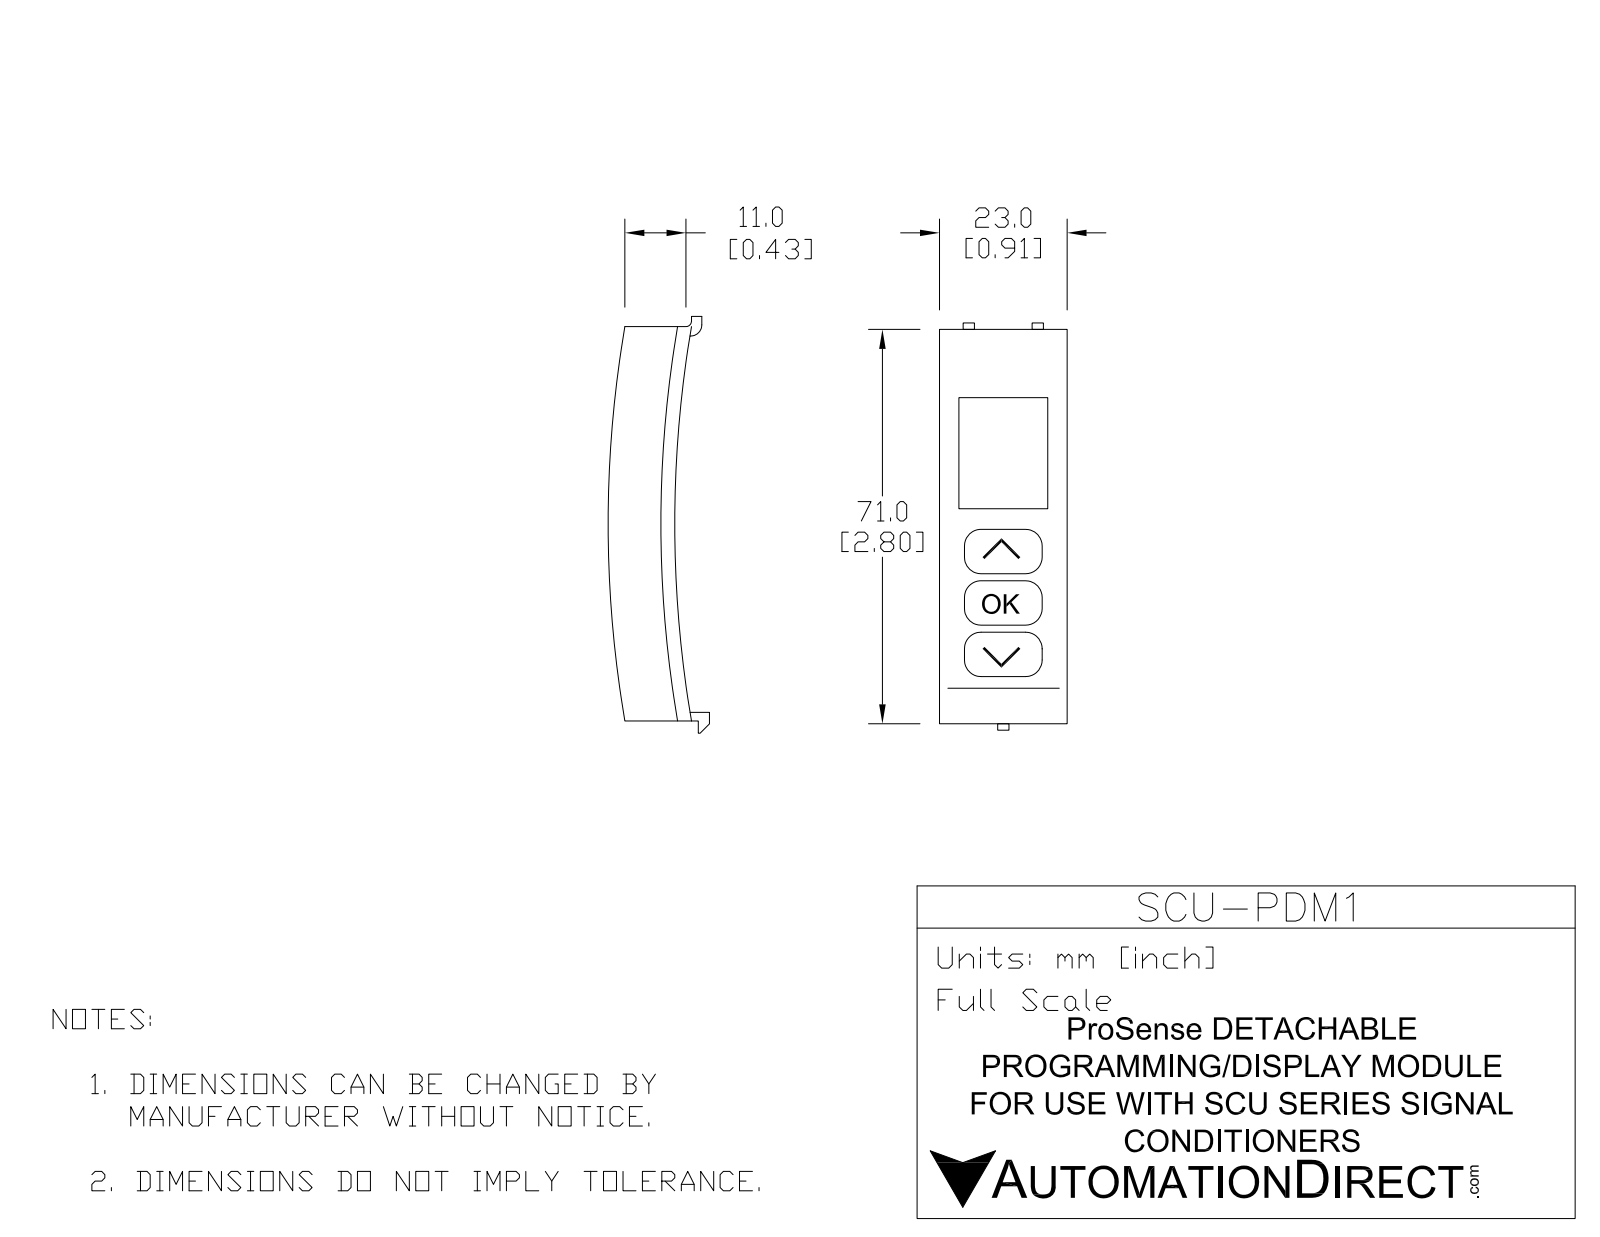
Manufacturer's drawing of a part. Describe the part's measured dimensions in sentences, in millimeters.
The part is named "SCU-PDM1". Its 3-D file was written by "SolidWorks 2017 (AUTOMOTIVE_DESIGN)". It is 1 solid with 63 faces: 39 planar, 12 cylindrical and 12 other. Overall it measures 75.05 by 27 by 18.26 millimeters. Its volume is 22 413 cubic millimeters and its surface area 6 480 square millimeters. Partial cylindrical surfaces (rounded edges, fillets, slot ends): 3 of radius 210.43, 1 of radius 1, 1 of radius 2. The main face-to-face distances are 27, 71, 5.5, 21.5, 2.02, 6.21, 8, 16, 12.49, 14.51.
